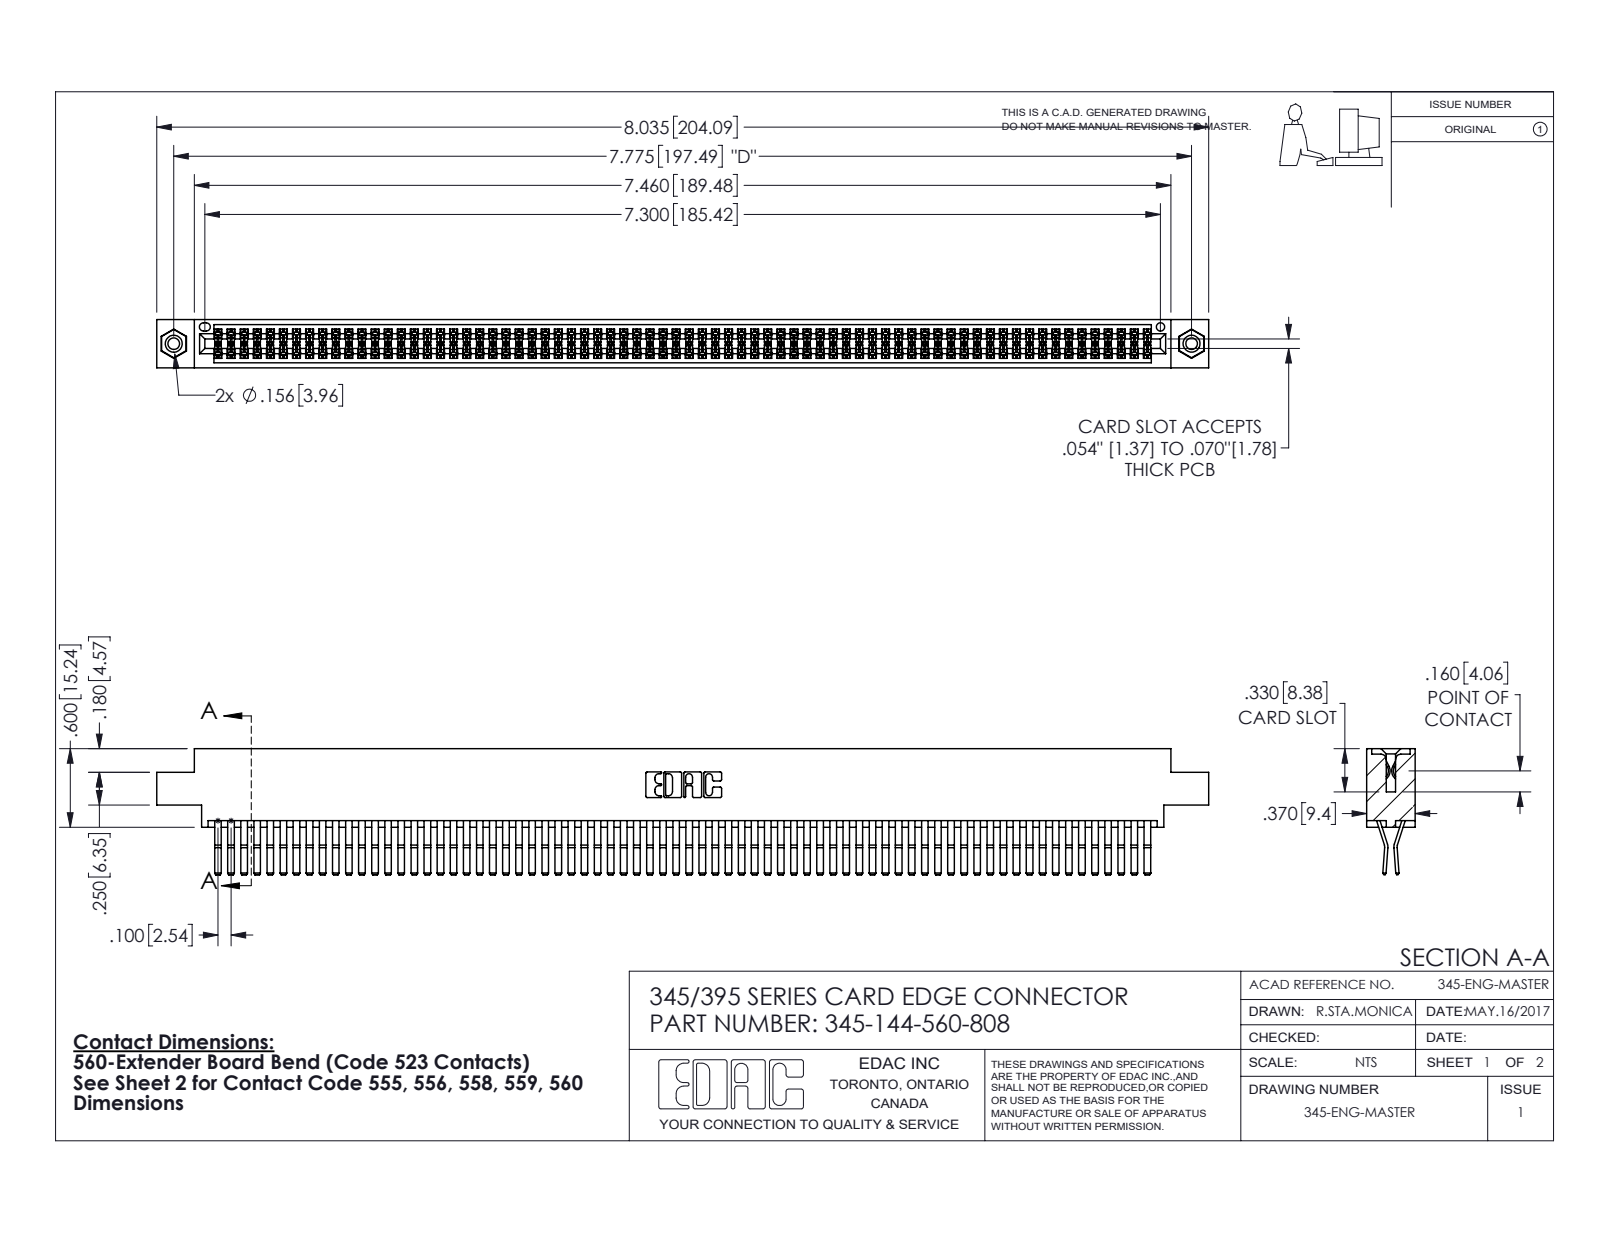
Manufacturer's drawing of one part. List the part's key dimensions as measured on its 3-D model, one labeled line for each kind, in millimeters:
Part name (STEP PRODUCT): 345-250-001_345-250-003-102; 345 Part_0.170 Offset - 0.156 Dia-TI; 345-144-560-808; 345-292-001_560 Tail
STEP written by: SolidWorks 2016 (CONFIG_CONTROL_DESIGN)
Units: millimetres
Bodies: 147 solids, 7678 faces (4868 planar, 2794 cylindrical, 16 other)
Overall size (bounding box): 204.1 × 24.4 × 9.4
Volume: 20 930 mm³ · Surface area: 34 100 mm²
Round holes (diameter × count): ⌀2.3 ×2, ⌀3.2 ×2, ⌀4 ×2, ⌀1.6 ×1
Round bosses / shafts (diameter × count): ⌀3.9 ×2
Partial cylindrical surfaces — rounded edges, fillets, slot ends (radius × count): R0.2 ×217, R0.3 ×22, R0.2 ×6, R0.8 ×6, R0.7 ×3, R0.3 ×2, R0.4 ×2, R0.5 ×2
Main face-to-face distances: 0.6, 1.8, 7.6, 9.4, 5.1, 2.5, 6.9, 5.7, 4.4, 3.8
Hole centre spacings: 6.9, 191.5, 197.5
